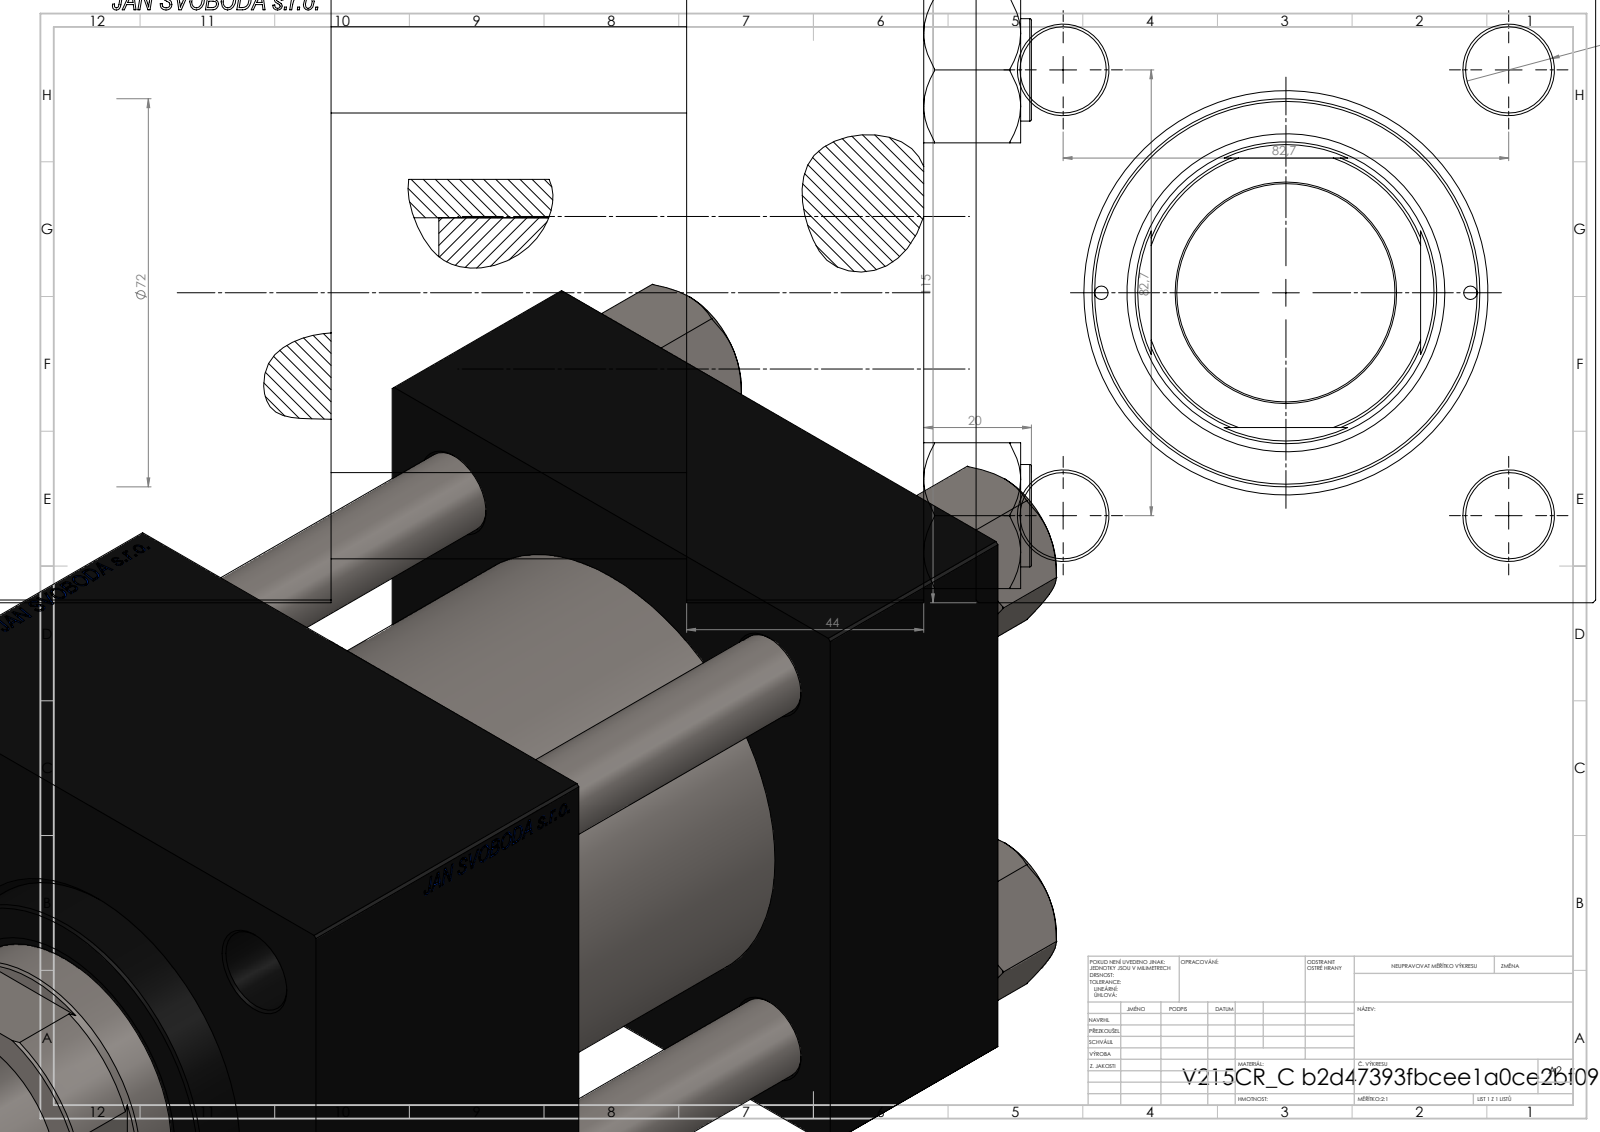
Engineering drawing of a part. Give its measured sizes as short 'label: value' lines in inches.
name: NUT_M5_C; V215CR_VCP_C; V215CR_C_TYCINKA; V215_VC_A (+1 more)
written by: SolidWorks 2019 (CONFIG_CONTROL_DESIGN)
unit: in
bodies: 11 solids, 1199 faces (575 planar, 88 cylindrical, 536 other)
size: 9.055 × 4.528 × 4.528
volume: 113.6 in³; area: 434.7 in²
holes: 4× ⌀0.63, 2× ⌀0.098, 2× ⌀0.276, 2× ⌀1.041, 2× ⌀1.378, 1× ⌀1.594, 1× ⌀2.205, 1× ⌀2.323, 1× ⌀2.402, 1× ⌀2.835, 1× ⌀3.15
bosses: 4× ⌀0.748, 1× ⌀3.386
rounds: 1× R1.063
face distances: 4.528, 1.732, 4.331, 2.598, 7.047, 5.315, 2.717, 0.787, 5.917, 4.185
hole spacings: 1.652, 2.302, 3.256, 3.393, 1.348, 4.605, 2.697, 4.37
